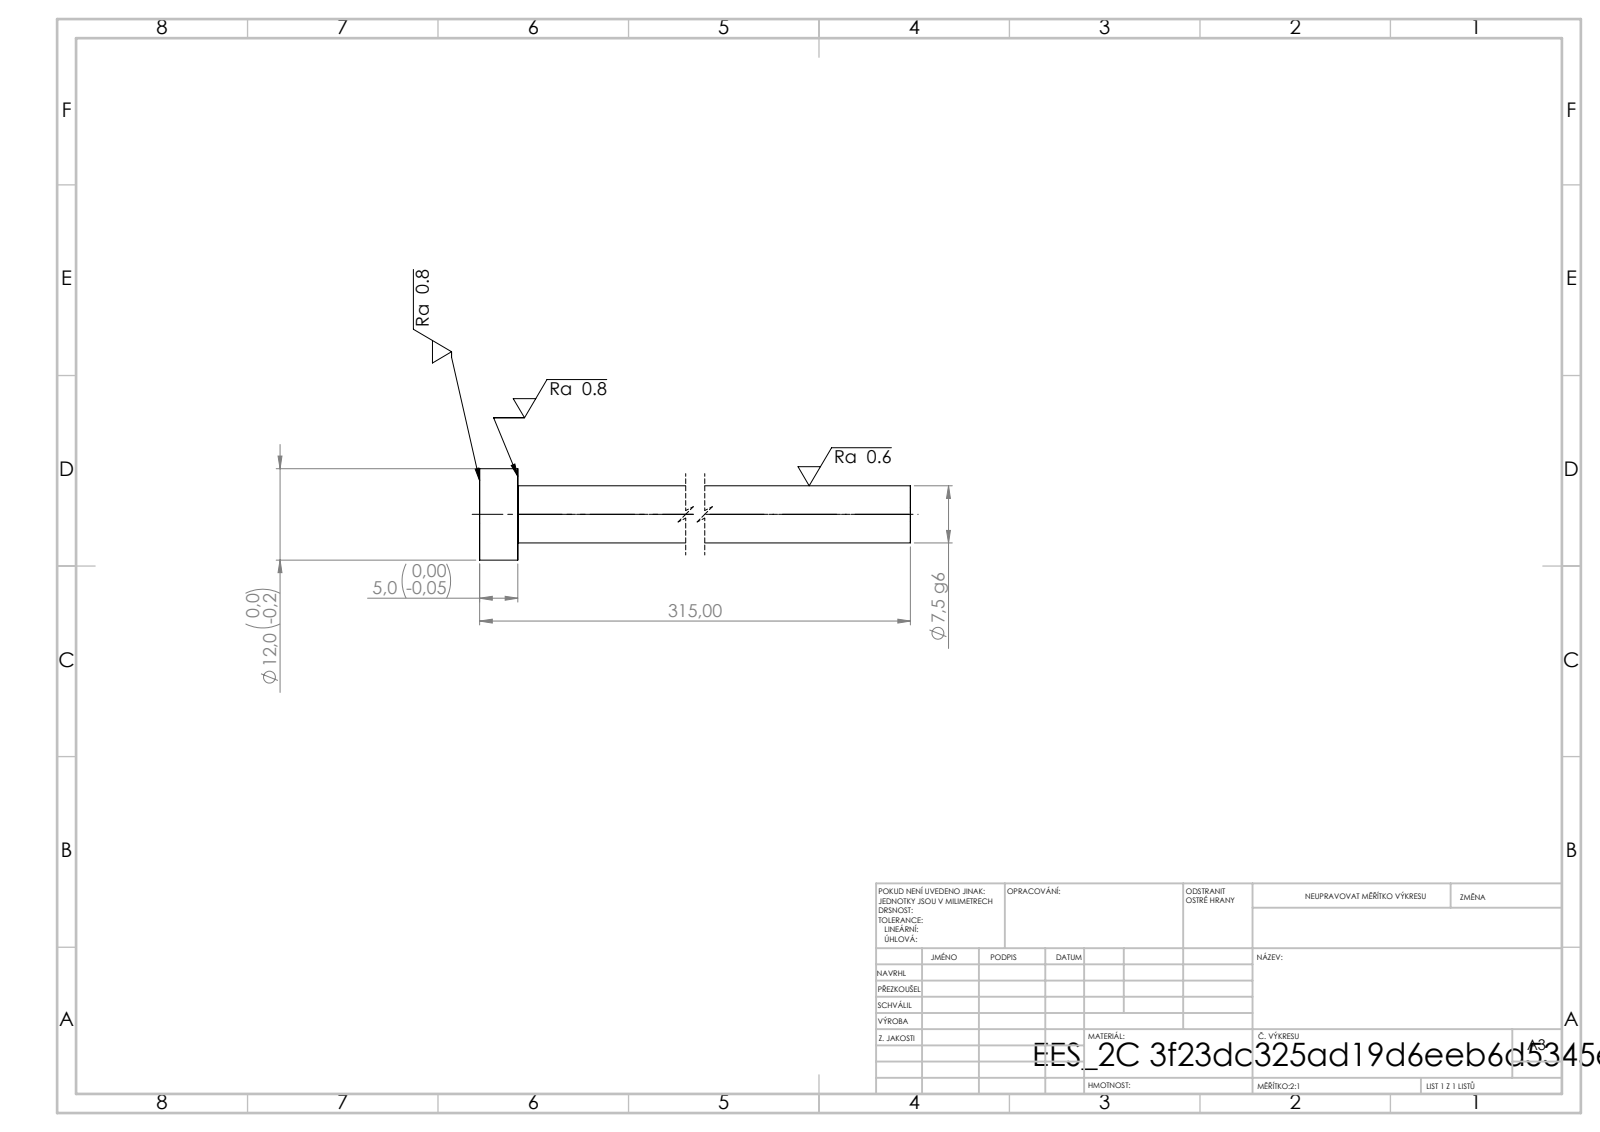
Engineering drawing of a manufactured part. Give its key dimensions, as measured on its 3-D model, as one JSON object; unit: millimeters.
{"step_written_by": "SolidWorks 2019 (CONFIG_CONTROL_DESIGN)", "units": "millimeters", "bodies": {"solids": 1, "faces": 7, "planar": 3, "cylindrical": 4, "other": 0}, "overall_size": [315, 12, 12], "volume_mm3": 14261, "surface_area_mm2": 7719, "round_bosses_or_shafts": [[12, 1], [7.5, 1]], "face_to_face_distances": [5, 315, 310]}
